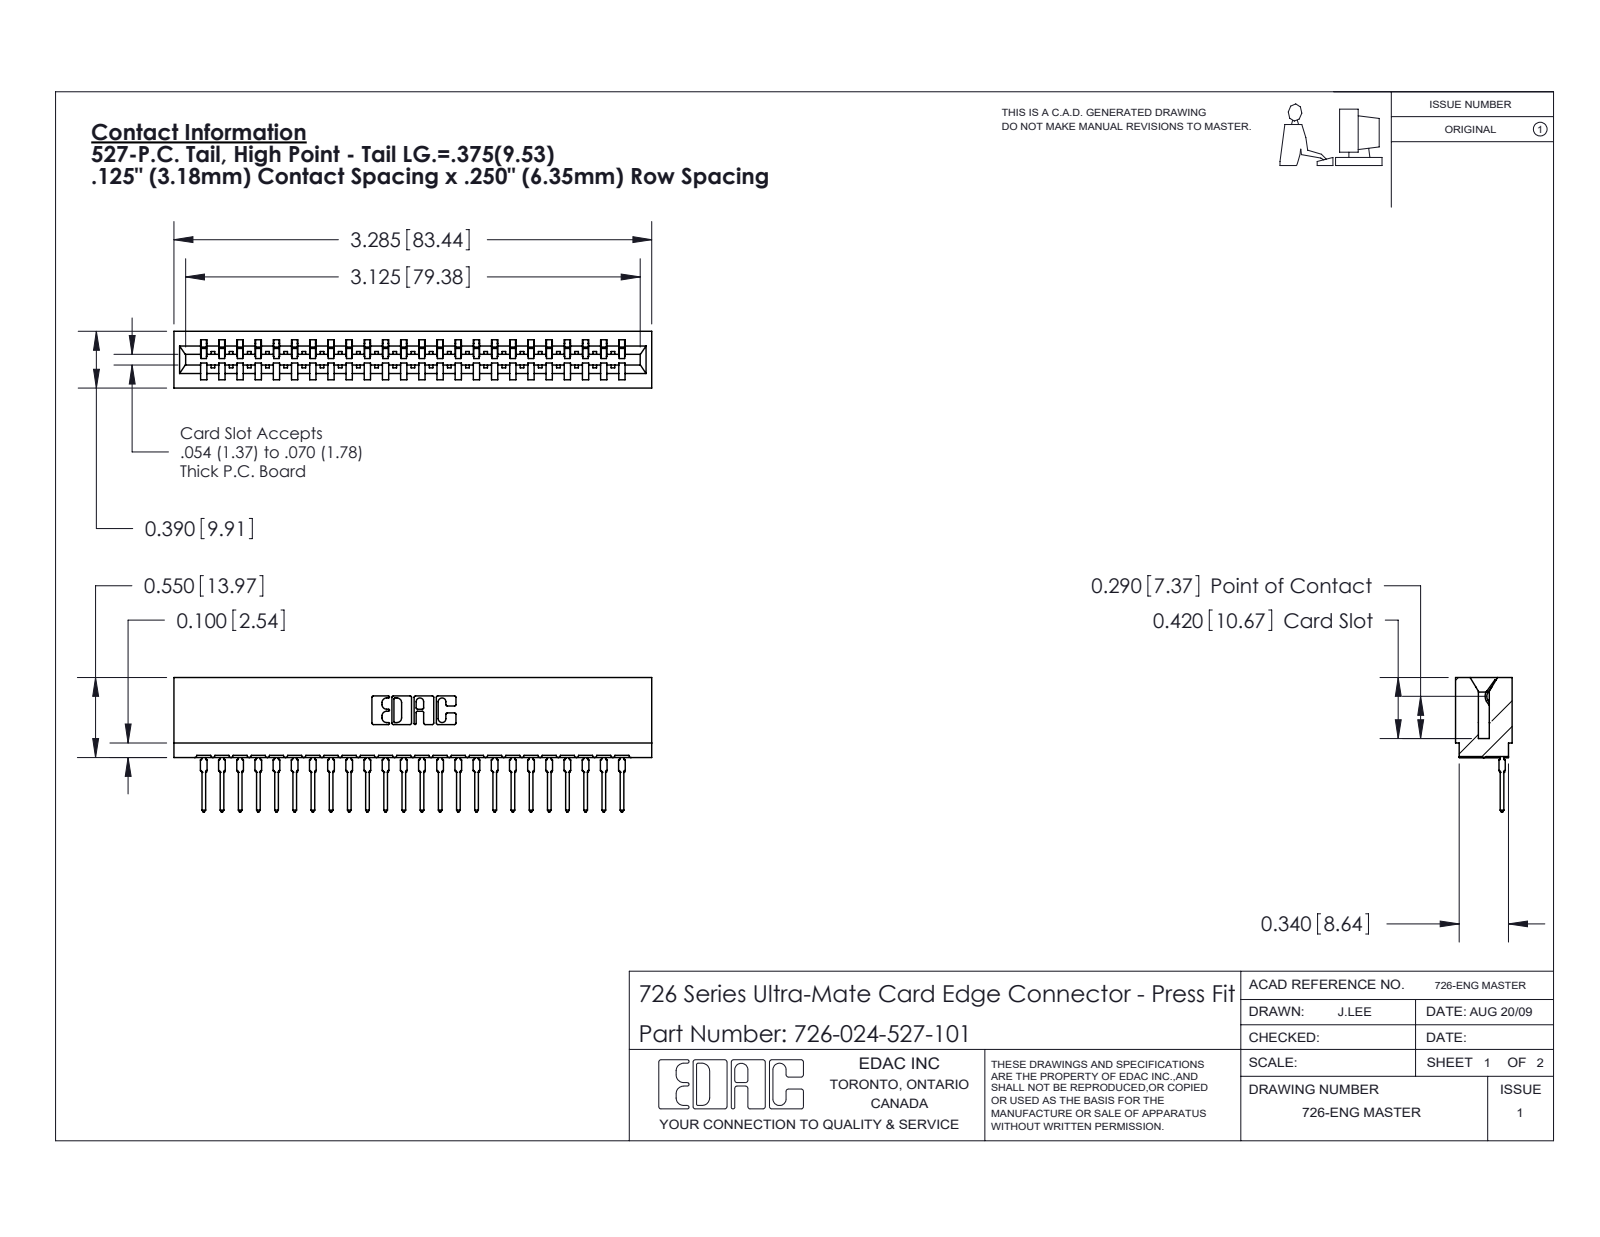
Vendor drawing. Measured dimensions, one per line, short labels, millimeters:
name: 746-292-001_527; 726-024-527-101; 726 Part_.515 Slot Depth - 01
written by: SolidWorks 2020 (CONFIG_CONTROL_DESIGN)
unit: mm
bodies: 25 solids, 2689 faces (1567 planar, 498 cylindrical, 624 other)
size: 83.4 × 23.5 × 9.9
volume: 7 570 mm³; area: 11 430 mm²
rounds: 48× R0.5, 25× R0.4, 22× R0.3, 6× R0.2, 6× R0.8, 4× R0.1, 4× R0.3, 3× R0.7
face distances: 1.4, 8.5, 9.9, 0.6, 6.4, 7.8, 1.1, 19.1, 2.1, 7
